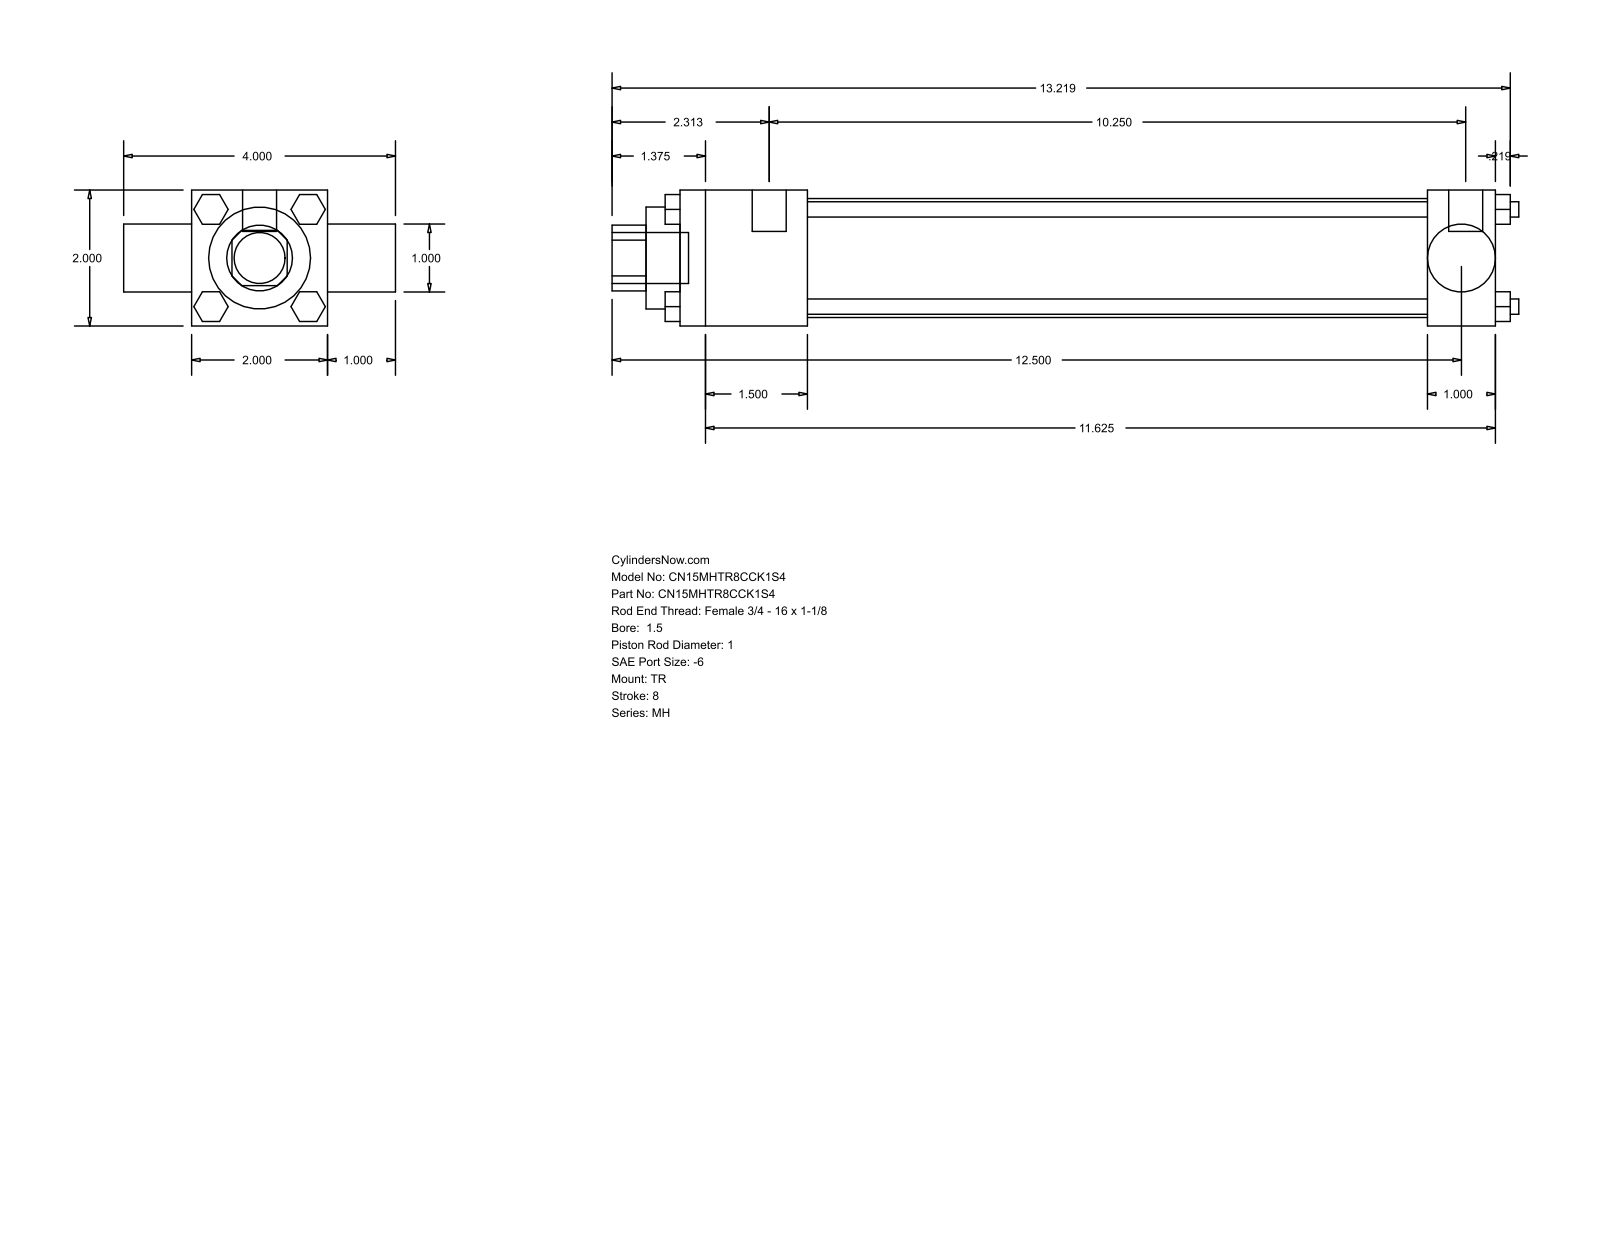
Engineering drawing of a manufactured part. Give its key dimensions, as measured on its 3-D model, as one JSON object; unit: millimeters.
{"part_name": "MH_TR__0150_1", "step_written_by": "GSSL Pune (CONFIG_CONTROL_DESIGN)", "units": "millimeters", "bodies": {"solids": 0, "faces": 120, "planar": 92, "cylindrical": 28, "other": 0}, "overall_size": [338.93, 101.6, 50.8], "round_holes": [[25.35, 1], [25.4, 1], [38.1, 1], [44.45, 1]], "round_bosses_or_shafts": [[5.71, 4], [5.56, 3], [12.7, 2], [19.05, 1]], "partial_cylinders_radius": [[12.29, 1]], "face_to_face_distances": [50.8, 25.4, 304.8, 76.2, 47.63, 257.17, 279.4, 231.77, 310.36, 12.7]}
